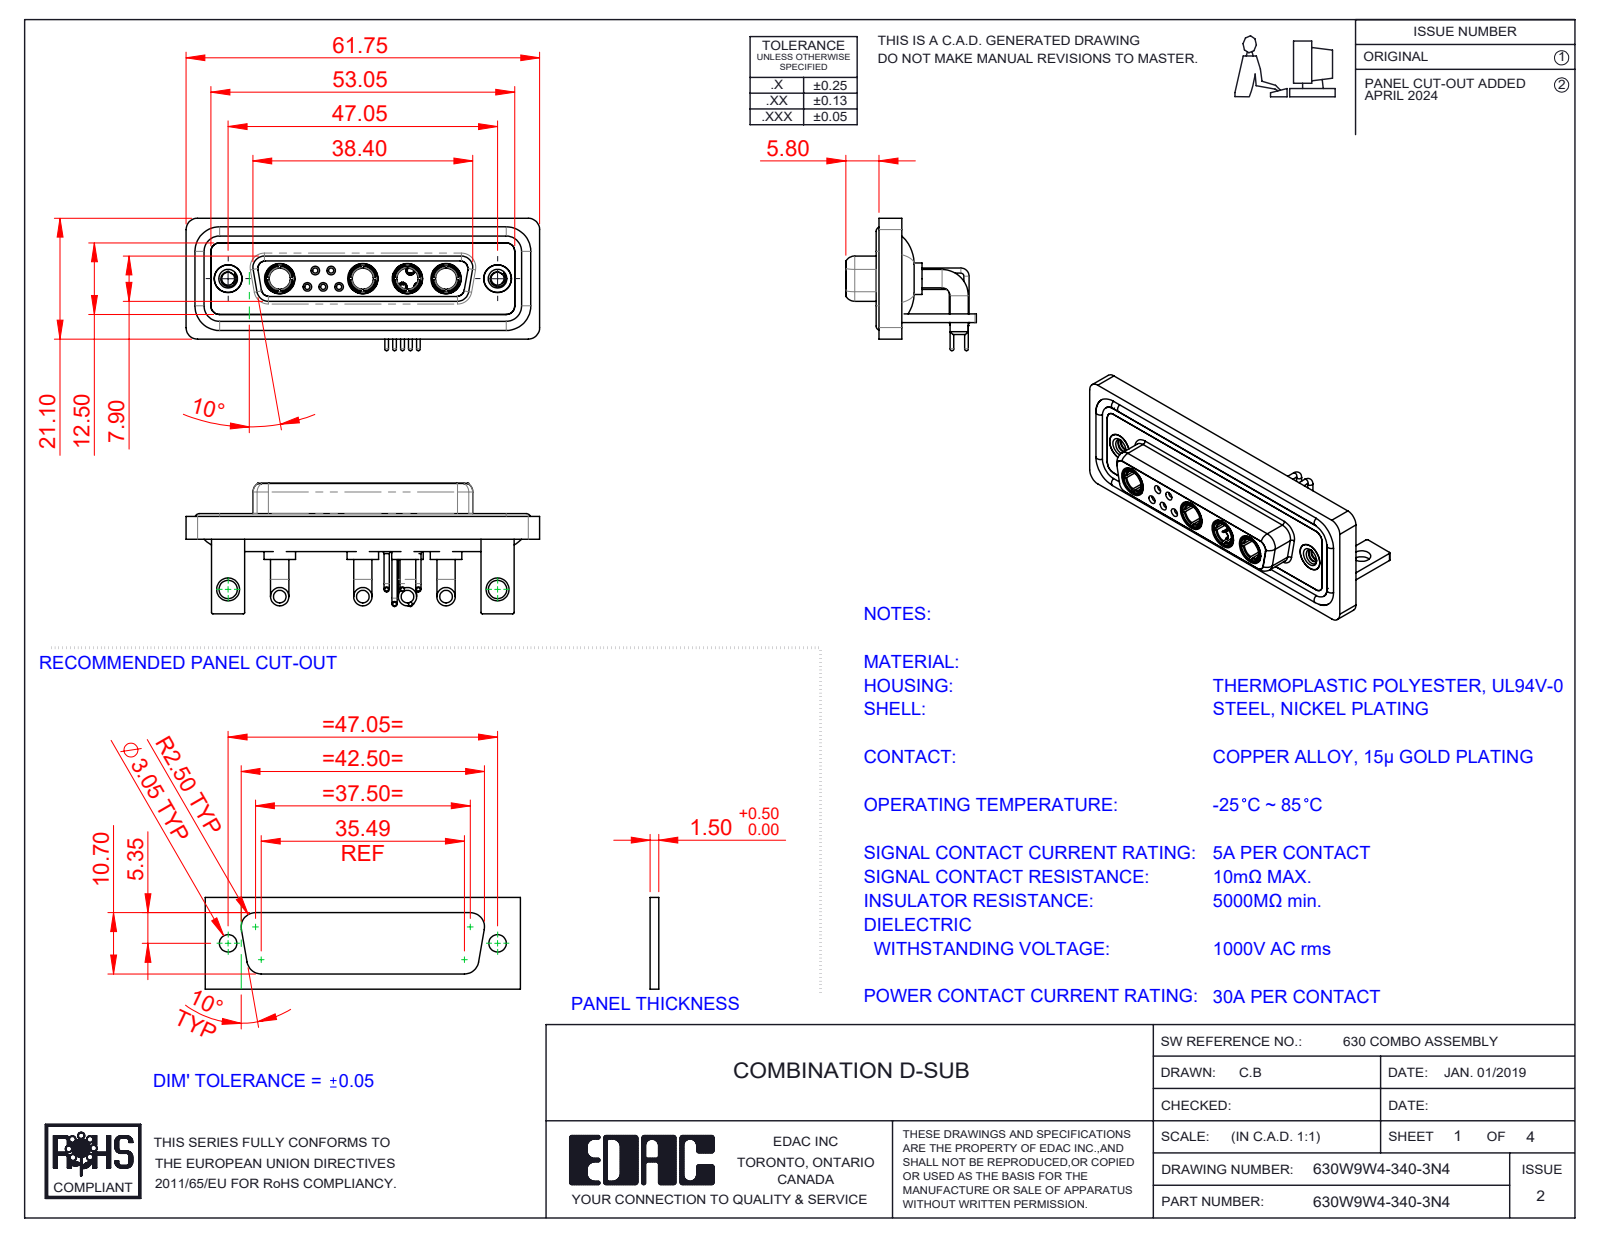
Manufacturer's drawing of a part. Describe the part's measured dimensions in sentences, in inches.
The part is named "630Combo Stabilizer Bracket_50 Contacts; 630W9W4-340-3N4; 630Combo Shell Rear_25 Contacts; 630Combo Shell Front_25 Contacts (+6 more)". Its 3-D file was written by "SolidWorks 2023 (CONFIG_CONTROL_DESIGN)". It is 22 solids with 1011 faces: 316 planar, 427 cylindrical and 268 other. Overall it measures 2.431 by 0.91 by 0.898 inches. Its volume is 0.545 cubic inches and its surface area 23.03 square inches. Round holes: 6 of diameter 0.191, 5 of diameter 0.035, 5 of diameter 0.043, 5 of diameter 0.059, 5 of diameter 0.079, 4 of diameter 0.146, 4 of diameter 0.209, 3 of diameter 0.063, 2 of diameter 0.067, 2 of diameter 0.089, 2 of diameter 0.126, 2 of diameter 0.157. Round bosses or shafts: 10 of diameter 0.035, 9 of diameter 0.063, 8 of diameter 0.126, 5 of diameter 0.079, 5 of diameter 0.059, 5 of diameter 0.026, 4 of diameter 0.217, 4 of diameter 0.205. Partial cylindrical surfaces (rounded edges, fillets, slot ends): 19 of radius 0.079, 18 of radius 0.059, 16 of radius 0.01, 8 of radius 0.053, 8 of radius 0.063, 5 of radius 0.02, 4 of radius 0.024, 4 of radius 0.026. The main face-to-face distances are 0.016, 0.071, 0.114, 0.146, 0.059, 0.161, 0.043, 0.055, 0.063, 0.098. The hole center spacings are 0.124, 0.109, 0.198, 0.545, 0.436, 0.504, 0.61, 0.218.
